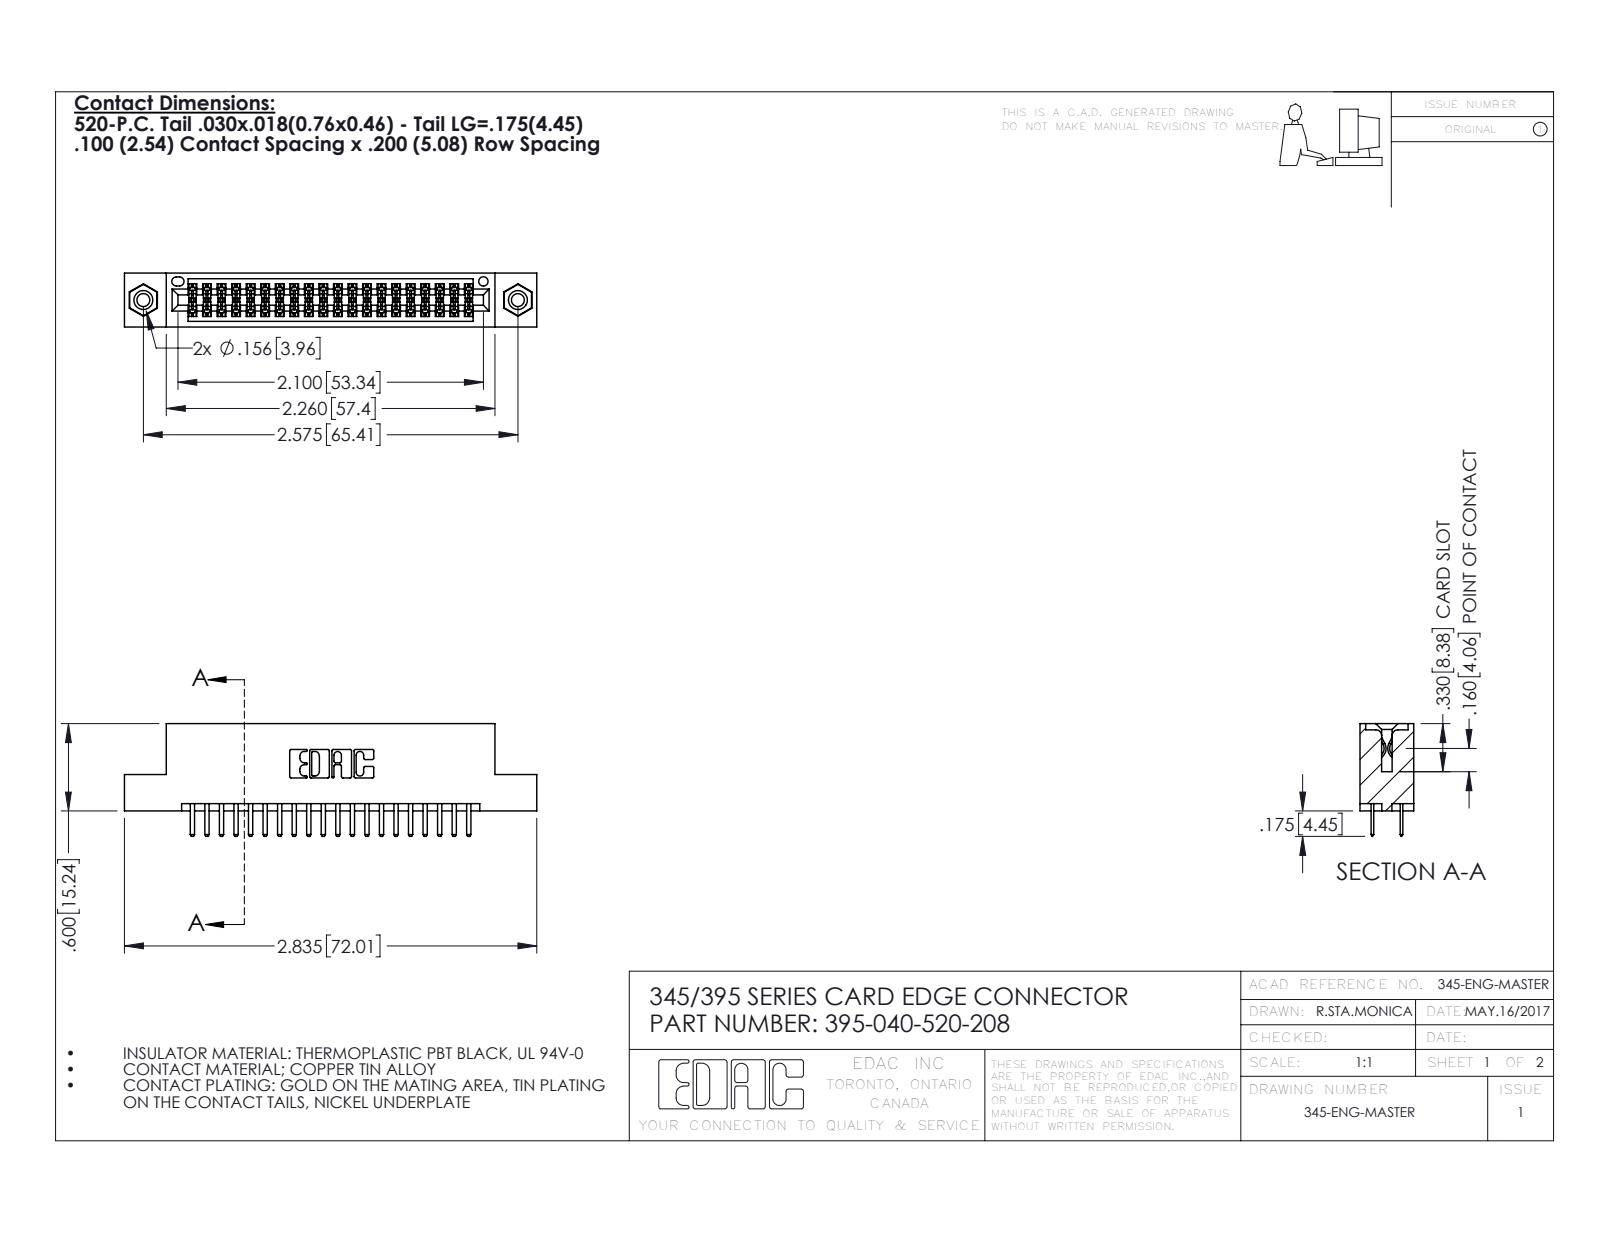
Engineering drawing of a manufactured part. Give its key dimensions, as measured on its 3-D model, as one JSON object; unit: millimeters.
{"part_name": "345-292-001_345-293-120; 395-040-520-208; 345-250-001_345-250-003-102; 345 Part_Flush Mounting Lugs - 0.156 Dia-TI", "step_written_by": "SolidWorks 2016 (CONFIG_CONTROL_DESIGN)", "units": "millimeters", "bodies": {"solids": 43, "faces": 2346, "planar": 1512, "cylindrical": 818, "other": 16}, "overall_size": [72, 19.7, 9.4], "volume_mm3": 6770, "surface_area_mm2": 9555, "round_holes": [[2.3, 2], [3.2, 2], [4, 2], [1.6, 1]], "round_bosses_or_shafts": [[3.9, 2]], "partial_cylinders_radius": [[0.2, 60], [0.3, 44], [0.3, 22], [0.2, 6], [0.8, 6], [0.7, 3], [0.4, 2], [0.5, 2]], "face_to_face_distances": [5.1, 1.8, 7.6, 9.4, 2.5, 6.9, 0.6, 5.7, 0.6, 1.8], "hole_center_spacings": [6.9, 59.5, 65.4]}
